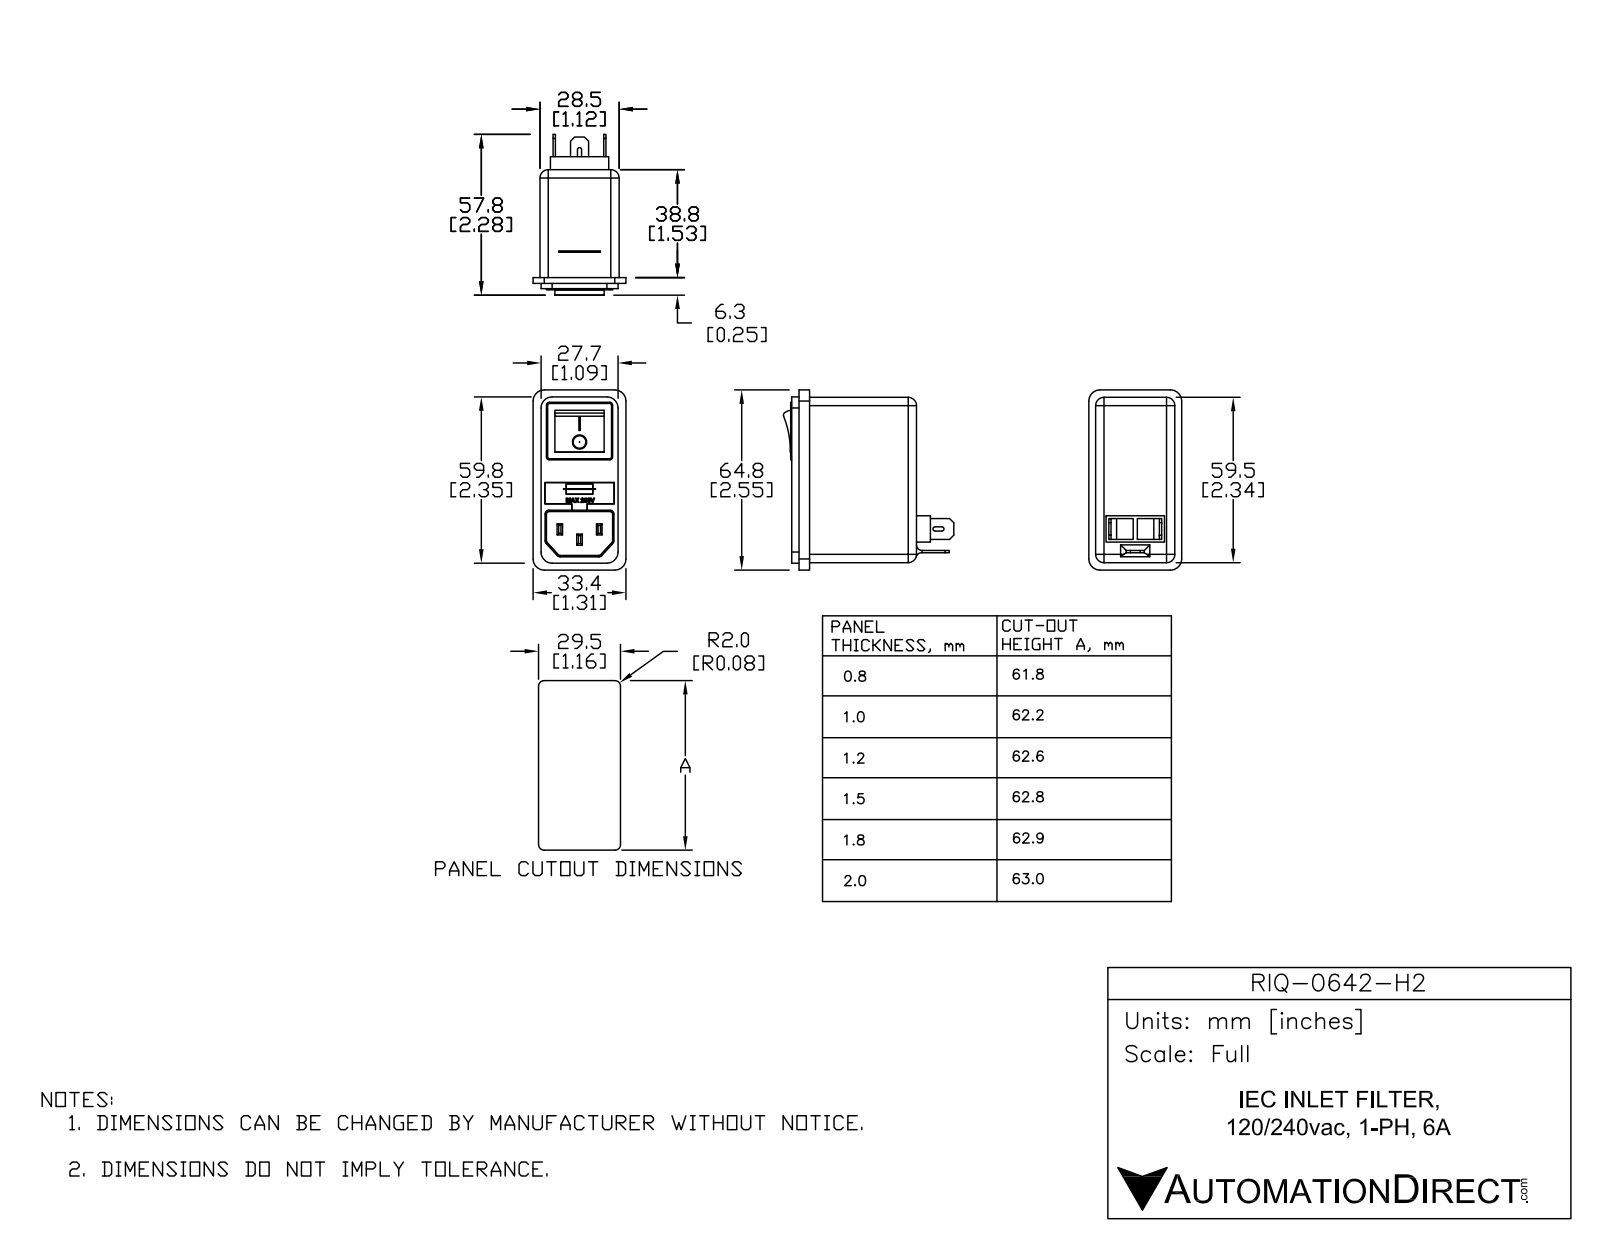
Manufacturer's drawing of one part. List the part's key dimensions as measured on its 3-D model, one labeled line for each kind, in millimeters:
Part name (STEP PRODUCT): RIQ0642H2
STEP written by: SolidWorks 2015 (AUTOMOTIVE_DESIGN)
Units: millimetres
Bodies: 5 solids, 397 faces (282 planar, 72 cylindrical, 43 other)
Overall size (bounding box): 64.8 × 61.48 × 33.4
Volume: 72 707 mm³ · Surface area: 17 741 mm²
Partial cylindrical surfaces — rounded edges, fillets, slot ends (radius × count): R0.6 ×11, R3 ×8, R0.1 ×6, R2 ×5, R0.15 ×4, R0.75 ×4, R4 ×4, R2.32 ×2
Main face-to-face distances: 28.5, 0.5, 2.25, 26.25, 0.4, 59.5, 44.9, 2.6, 1.75, 26.75
